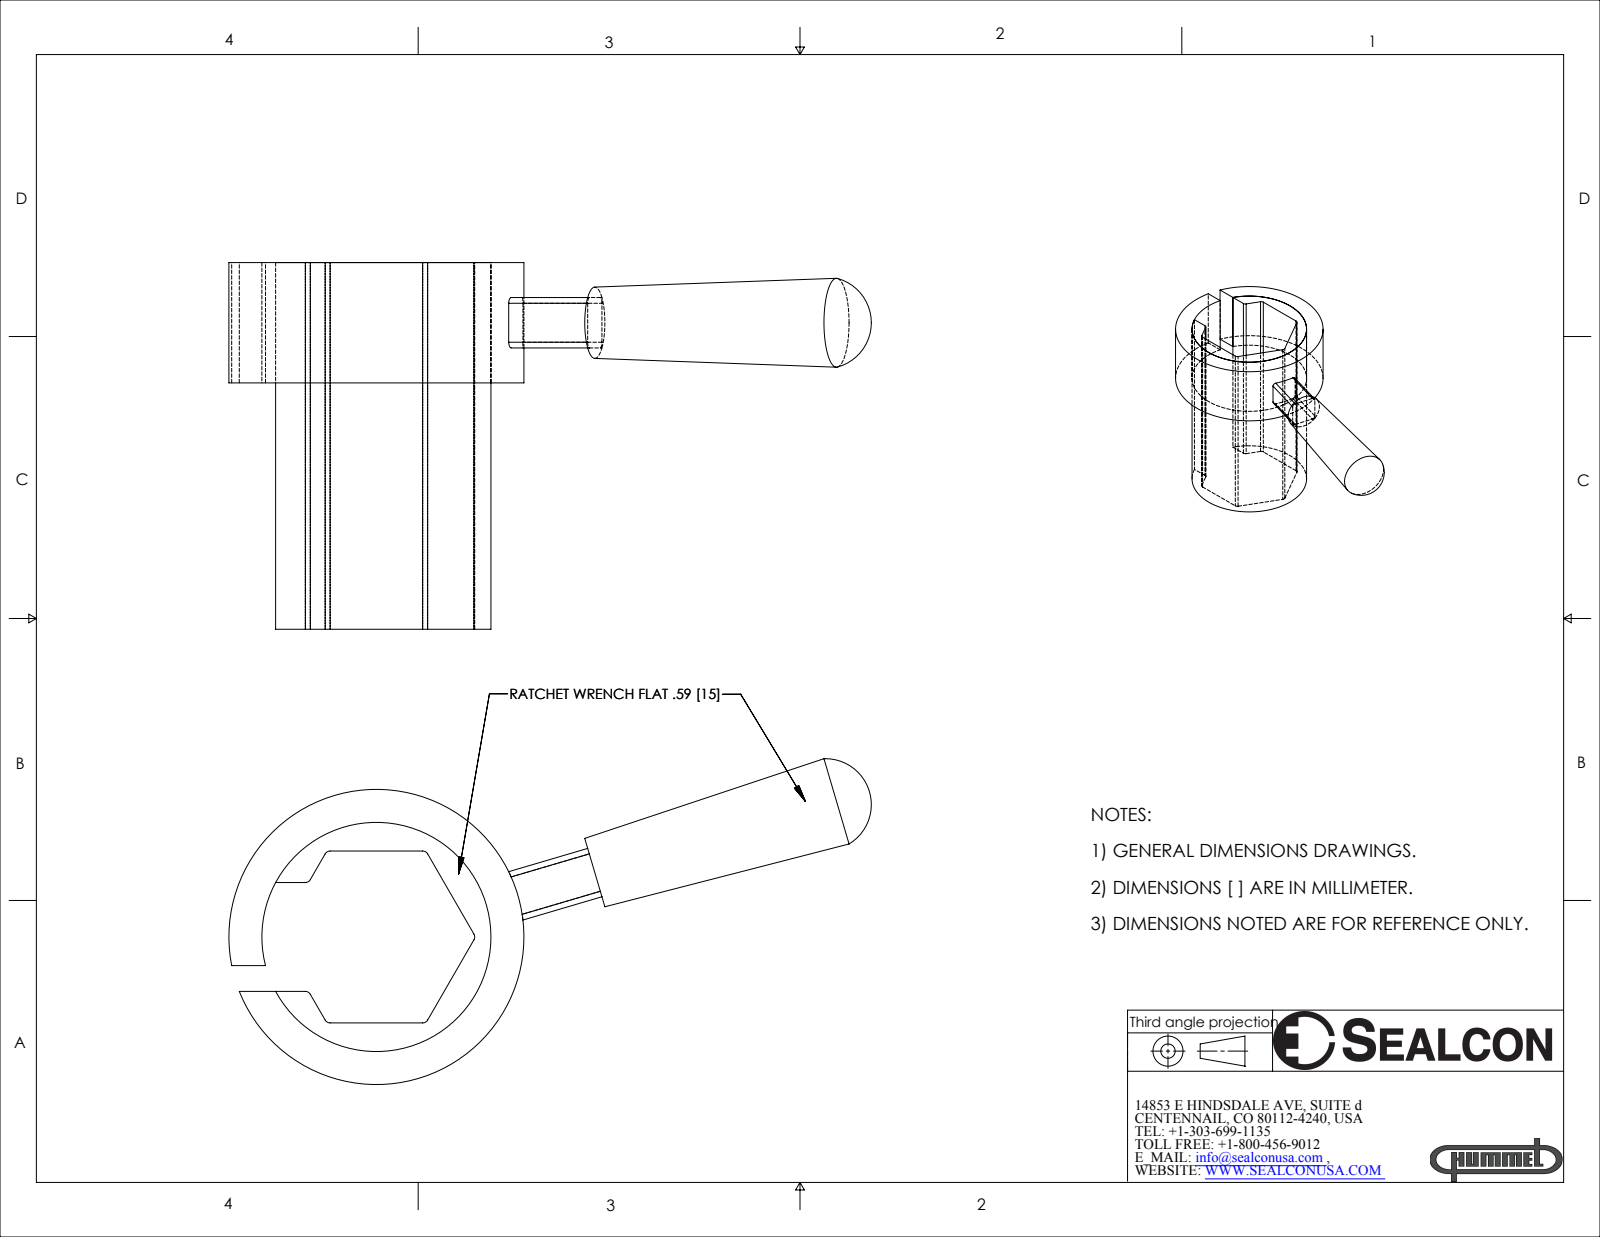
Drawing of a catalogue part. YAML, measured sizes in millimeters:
part_name: "R-1500-WR"
step_written_by: "SolidWorks 2007 (CONFIG_CONTROL_DESIGN)"
units: millimeters
bodies: {solids: 3, faces: 43, planar: 19, cylindrical: 20, other: 4}
overall_size: [56.09, 32, 28.44]
volume: 6283
surface_area: 6005
round_holes:
  - {diameter: 20, count: 1}
round_bosses_or_shafts:
  - {diameter: 25.76, count: 1}
partial_cylinders:
  - {radius: 0.5, count: 11}
face_to_face_distances: [15, 10.5, 2.75, 12.25, 21.5, 32, 9.5, 4.4, 3.05, 7.45]
